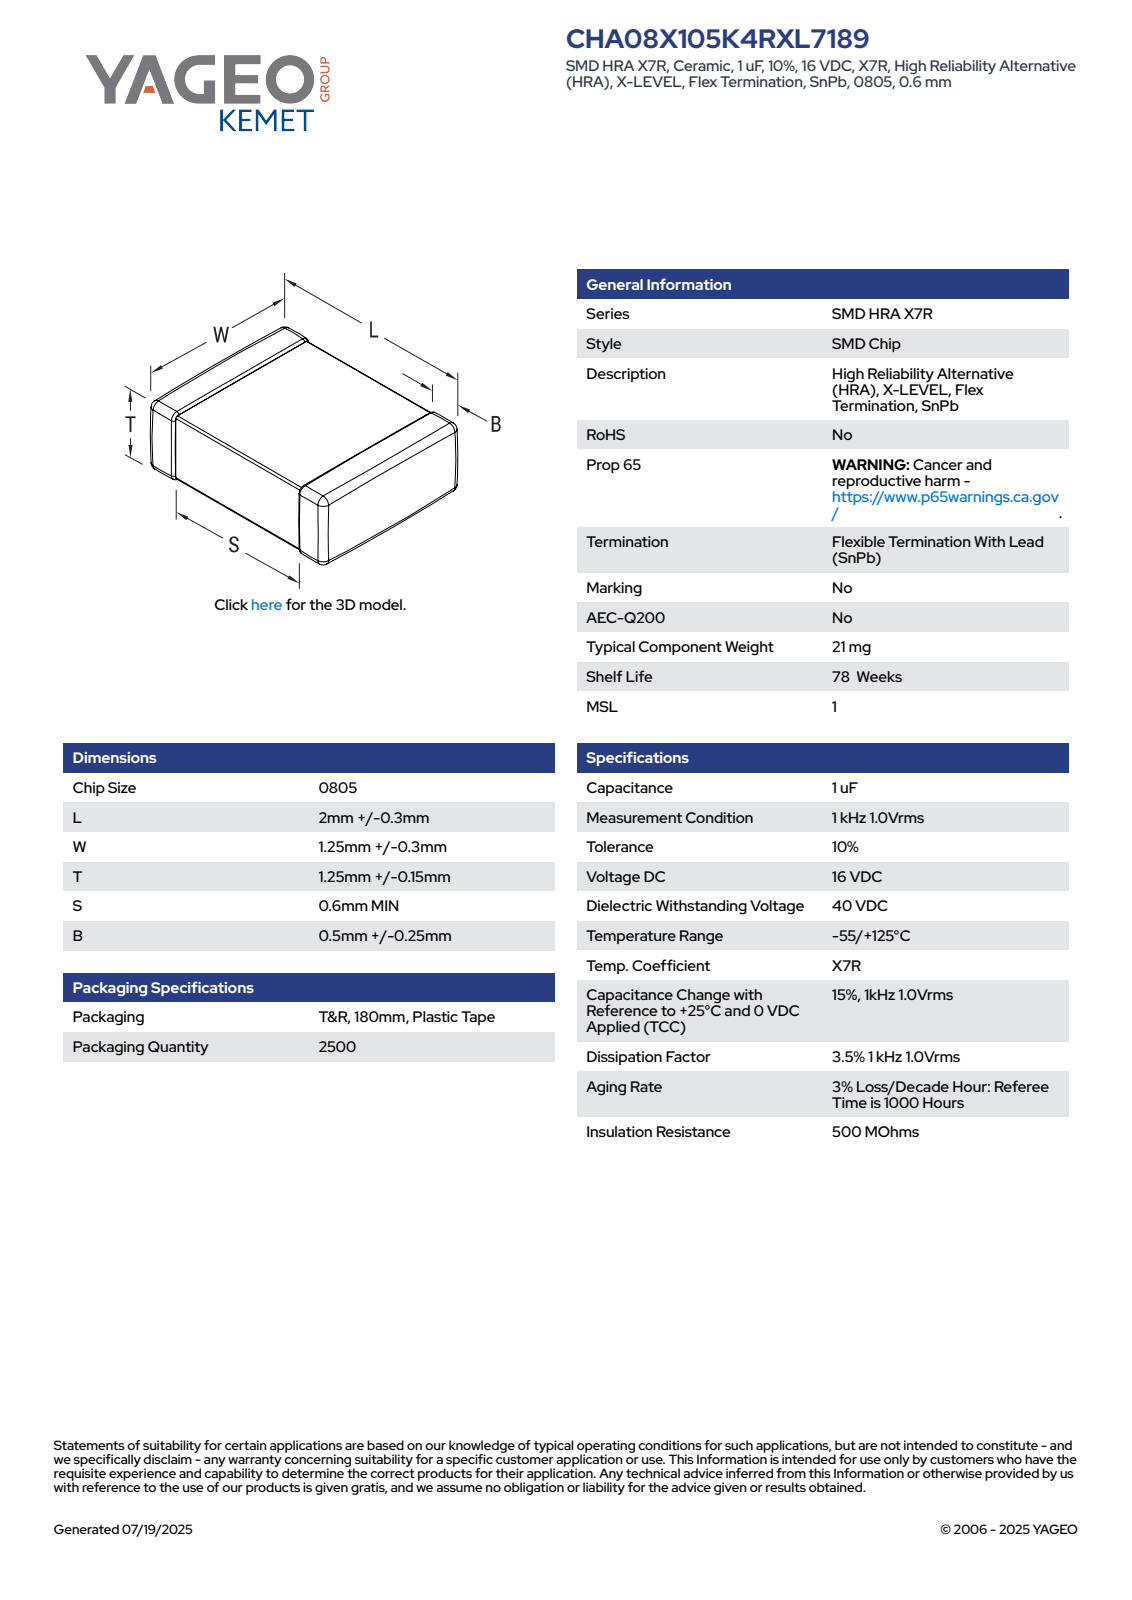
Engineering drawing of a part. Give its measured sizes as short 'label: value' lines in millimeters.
name: CCSM_STD_0805_L2.3W1.55T1.4S1.25B0.75
written by: SolidWorks 2021 (AUTOMOTIVE_DESIGN)
unit: mm
bodies: 4 solids, 121 faces (71 planar, 34 cylindrical, 16 other)
size: 2.3 × 1.55 × 1.4
volume: 5 mm³; area: 18 mm²
face distances: 1.37, 1.4, 1.52, 2.3, 1.55, 1.34, 1.49, 1.06, 1.24, 1.01
